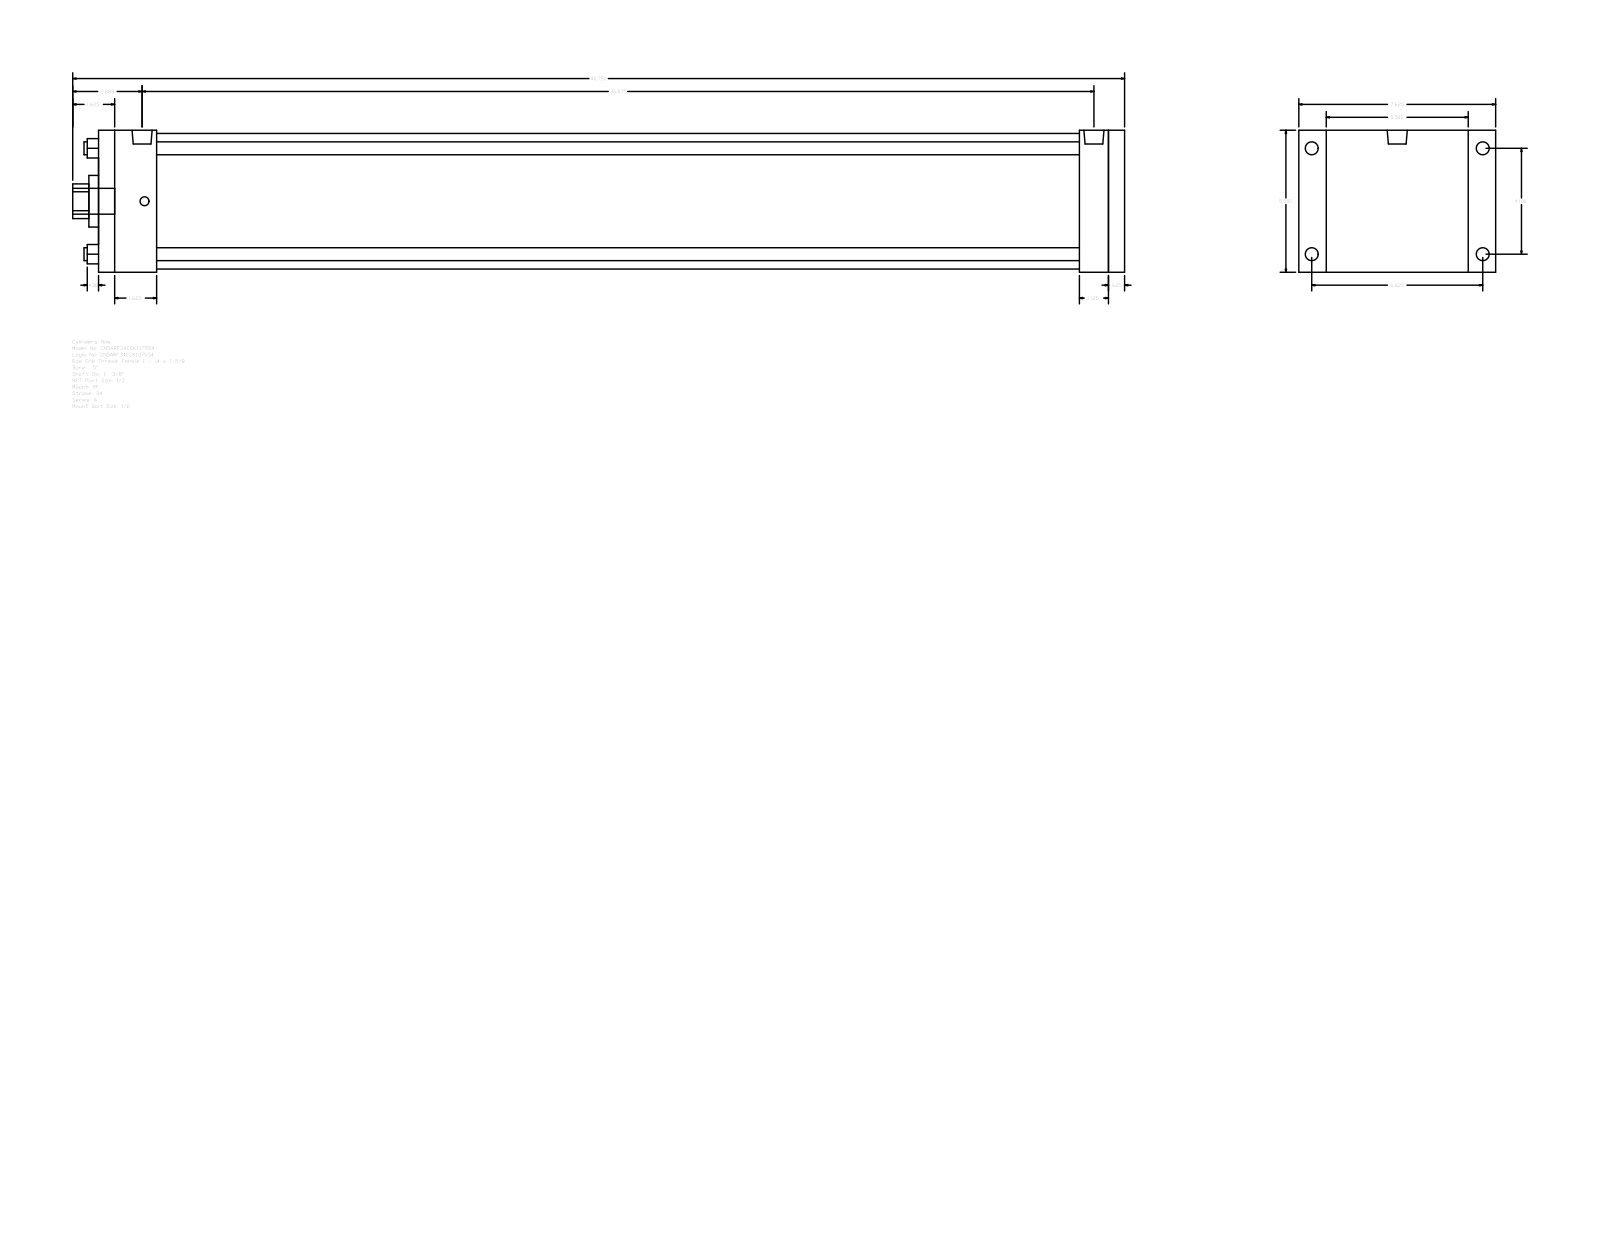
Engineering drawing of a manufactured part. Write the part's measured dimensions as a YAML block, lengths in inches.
part_name: "A_RF__0500_1.375"
step_written_by: "GSSL Pune (CONFIG_CONTROL_DESIGN)"
units: inches
bodies: {solids: 0, faces: 92, planar: 64, cylindrical: 28, other: 0}
overall_size: [40.75, 7.625, 5.5]
round_holes:
  - {diameter: 0.5, count: 4}
  - {diameter: 1.375, count: 1}
  - {diameter: 2, count: 1}
  - {diameter: 5.25, count: 1}
round_bosses_or_shafts:
  - {diameter: 0.5, count: 4}
  - {diameter: 0.344, count: 4}
  - {diameter: 0.778, count: 2}
  - {diameter: 1, count: 1}
partial_cylinders:
  - {radius: 0.672, count: 1}
face_to_face_distances: [5.5, 39.75, 0.625, 39.125, 1.125, 2.25, 36.875, 37.5, 38, 35.75]
hole_center_spacings: [2.899, 4.1, 5.798]
